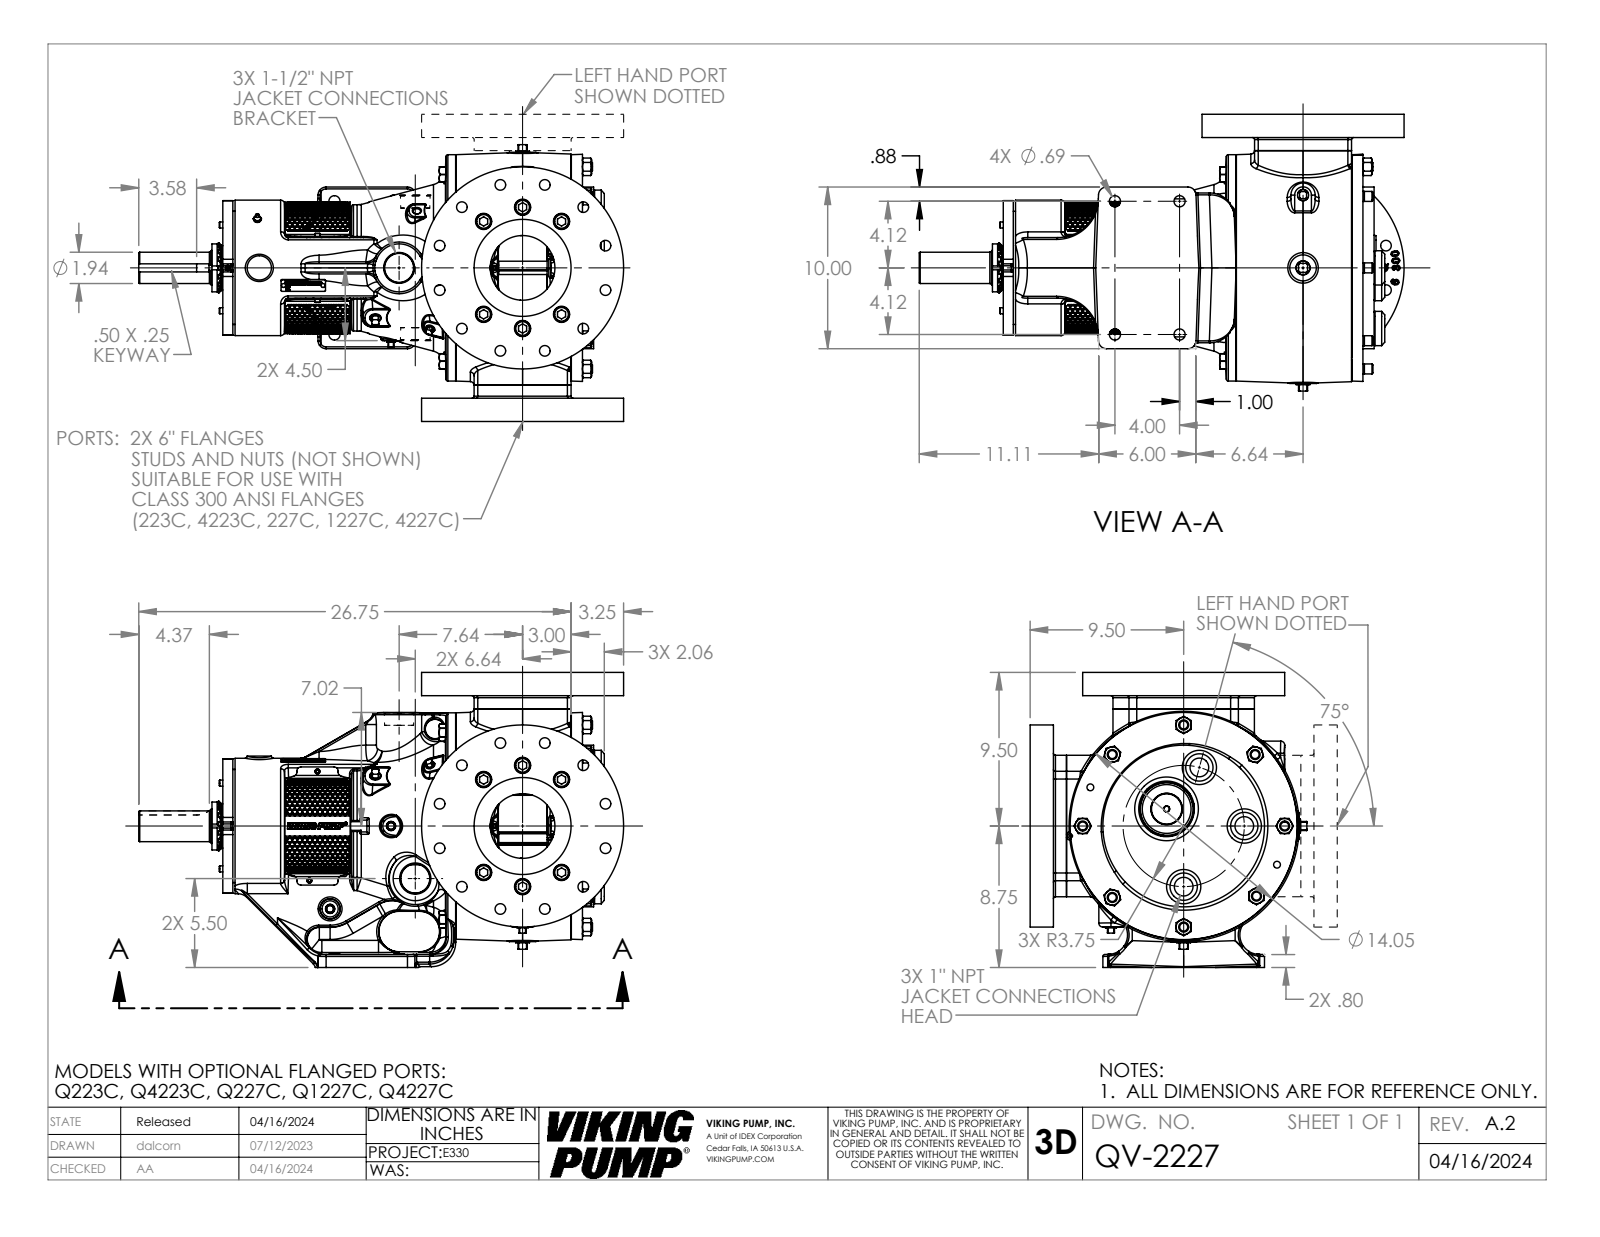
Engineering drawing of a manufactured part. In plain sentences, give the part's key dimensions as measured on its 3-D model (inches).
The part is named "QV-2227". Its 3-D file was written by "SolidWorks 2022 (AUTOMOTIVE_DESIGN)". It is 1 solid with 3878 faces: 1345 planar, 734 cylindrical and 1799 other. Overall it measures 29.999 by 18.25 by 17.121 inches. Its volume is 2 603 cubic inches and its surface area 2 545 square inches. Round holes: 36 of diameter 0.656, 12 of diameter 1, 9 of diameter 0.25, 8 of diameter 0.266, 8 of diameter 1.157, 4 of diameter 0.688, 3 of diameter 1.156, 3 of diameter 1.85, 2 of diameter 0.159, 2 of diameter 0.313, 2 of diameter 0.33, 2 of diameter 0.422. Round bosses or shafts: 12 of diameter 0.937, 11 of diameter 0.625, 8 of diameter 0.617, 3 of diameter 2.12, 3 of diameter 1.75, 3 of diameter 0.312, 3 of diameter 0.19, 2 of diameter 12.5. Partial cylindrical surfaces (rounded edges, fillets, slot ends): 52 of radius 0.12, 18 of radius 0.015, 18 of radius 0.092, 18 of radius 0.25, 16 of radius 0.07, 16 of radius 0.75, 14 of radius 0.5, 10 of radius 0.24. The main face-to-face distances are 1.44, 0.691, 16.81, 18.25, 3.75, 22.254, 22.944, 2.25, 18.504, 19.194. The hole center spacings are 5.313, 3.75, 10.263, 2.75, 9.202, 2.079, 3.133, 5.932.
